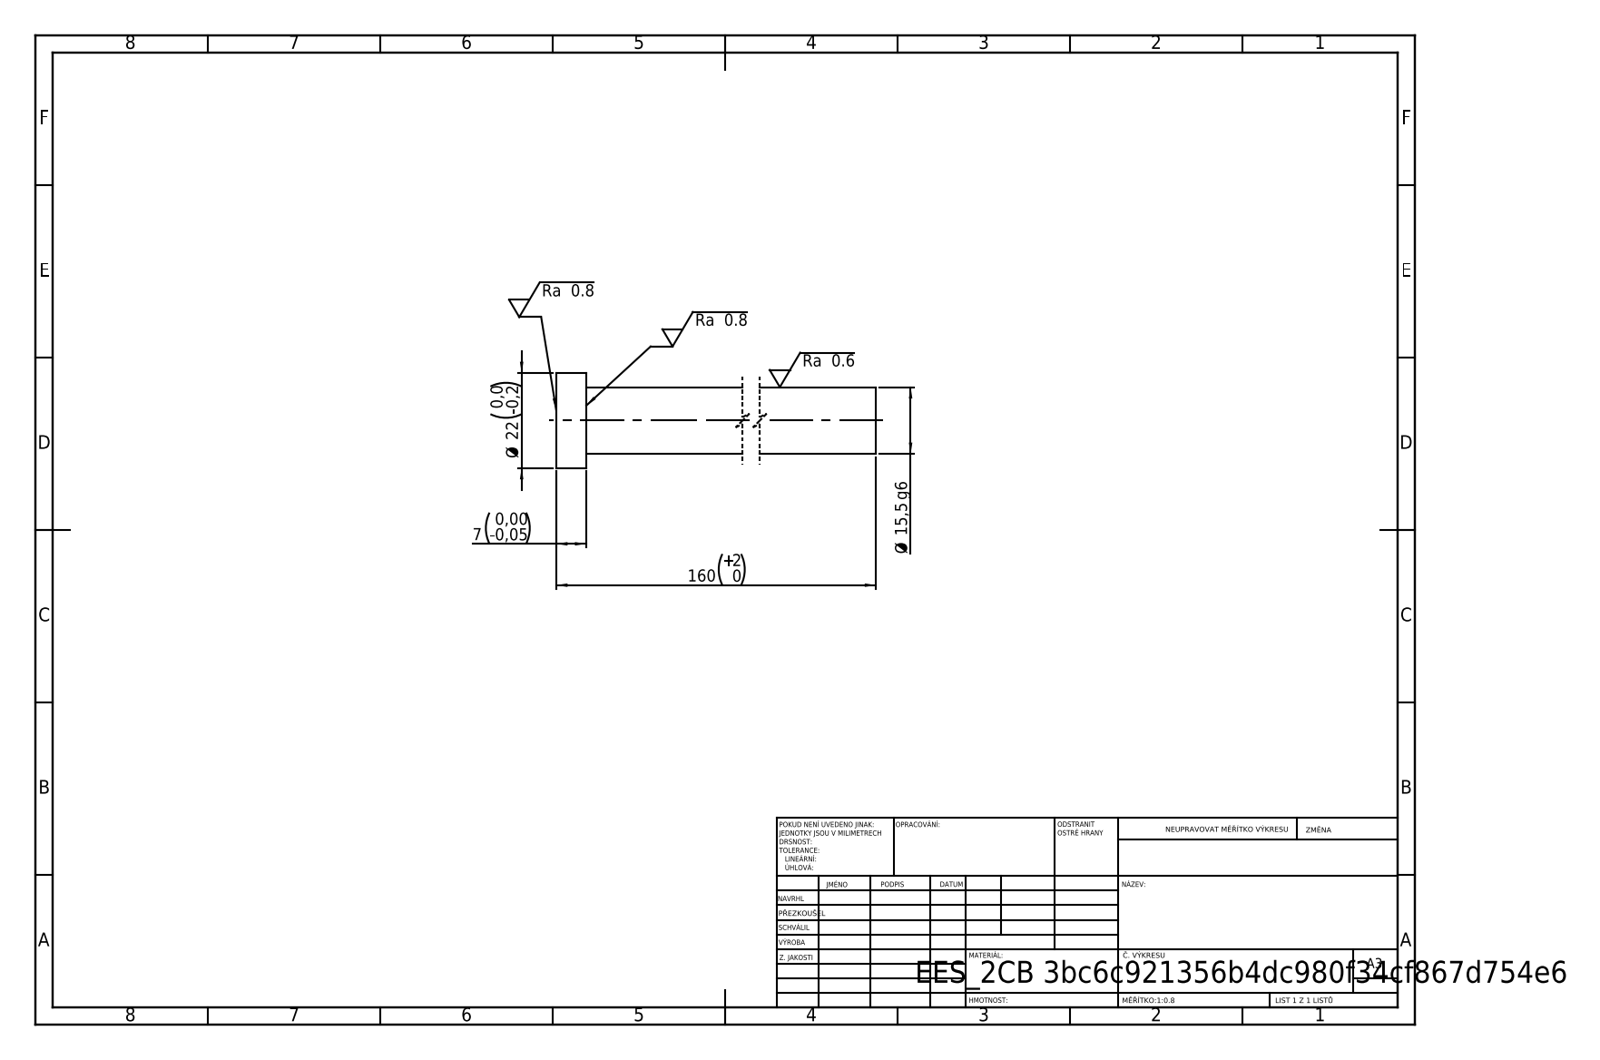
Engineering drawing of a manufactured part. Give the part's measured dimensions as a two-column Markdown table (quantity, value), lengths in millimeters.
| quantity | value |
| --- | --- |
| STEP written by | SolidWorks 2019 (CONFIG_CONTROL_DESIGN) |
| units | millimeters |
| bodies | 1 solid, 7 faces (3 planar, 4 cylindrical, 0 other) |
| overall size | 160 × 22 × 22 |
| volume | 31 531 mm³ |
| surface area | 8 694 mm² |
| round bosses / shafts (diameter × count) | 22 × 1, 15.5 × 1 |
| main face-to-face distances | 7, 160, 153 |
